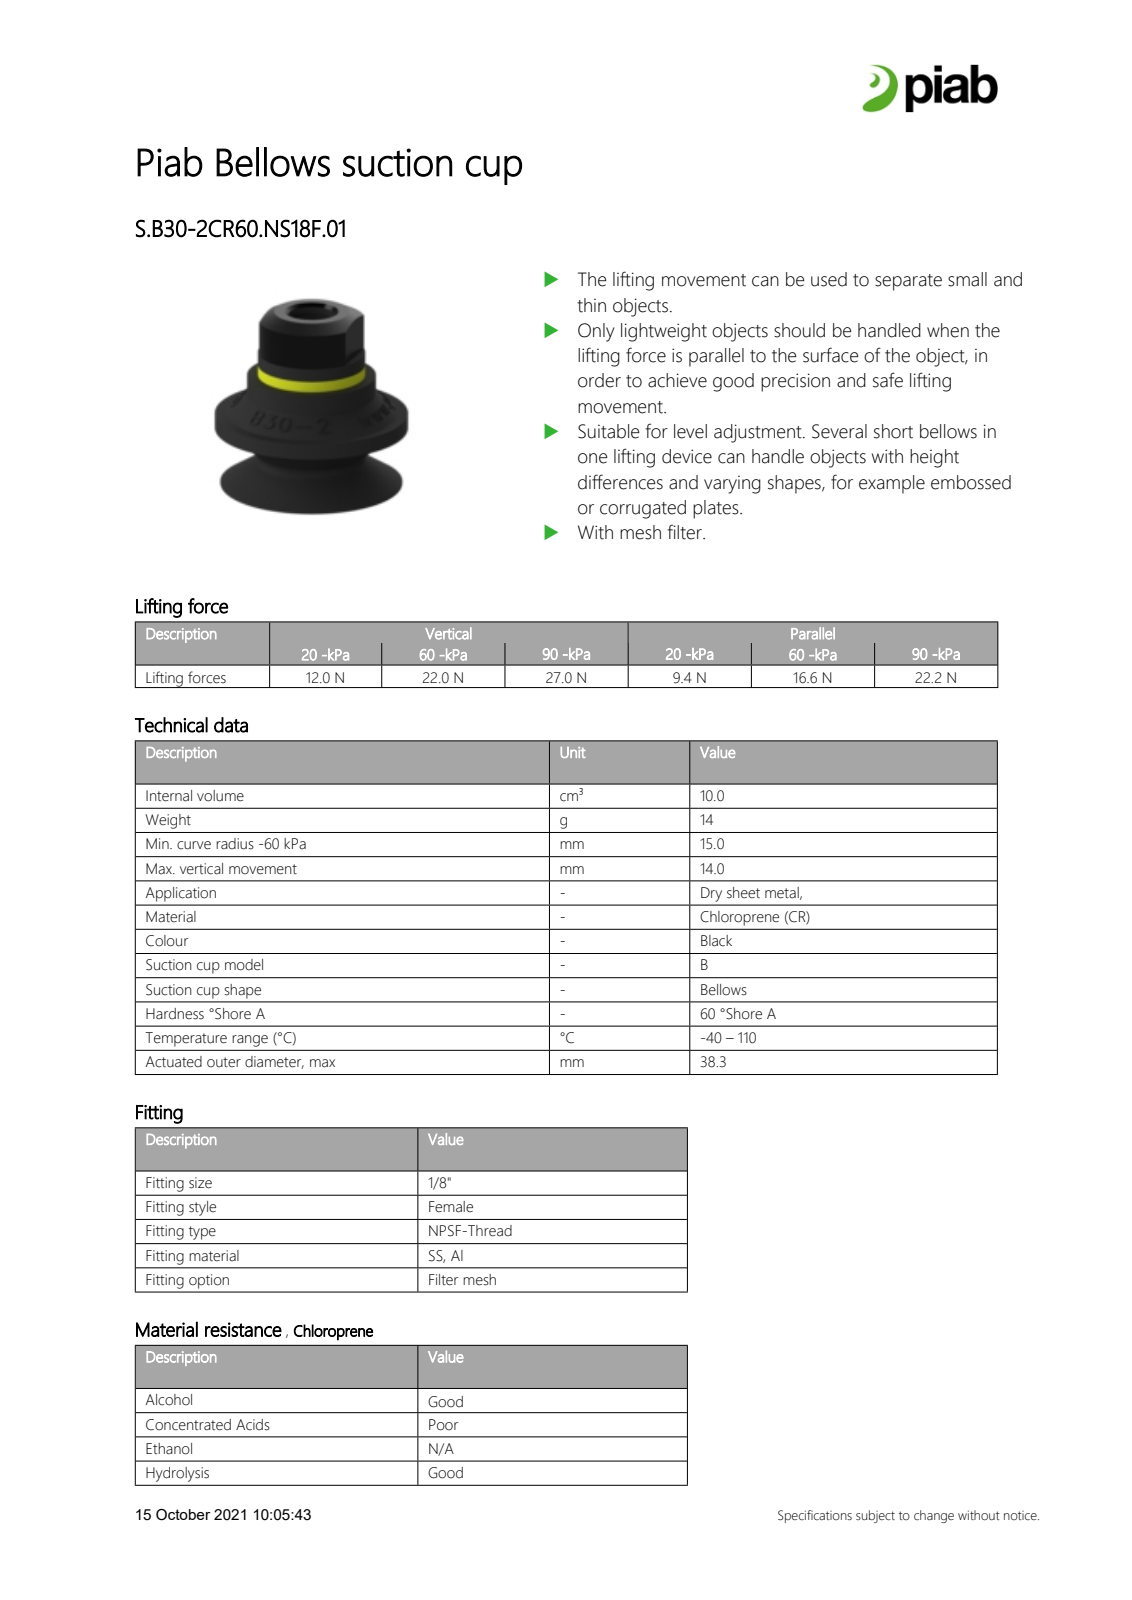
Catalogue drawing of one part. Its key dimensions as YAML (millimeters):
part_name: "S_A006_B012; A006_B30-2; B012_Fitting 40 04AA"
step_written_by: "ST-DEVELOPER v16.7 (AUTOMOTIVE_DESIGN)"
units: millimeters
bodies: {solids: 2, faces: 697, planar: 423, cylindrical: 59, other: 215}
overall_size: [36, 36, 34.2]
volume: 14145
surface_area: 7354
round_holes:
  - {diameter: 6.35, count: 1}
  - {diameter: 8.7, count: 1}
  - {diameter: 10, count: 1}
round_bosses_or_shafts:
  - {diameter: 36, count: 1}
  - {diameter: 34, count: 1}
  - {diameter: 24, count: 1}
  - {diameter: 20, count: 1}
partial_cylinders:
  - {radius: 0.5, count: 49}
face_to_face_distances: [14.2, 26.2, 12, 15, 8, 3, 11.2, 19.2, 5, 7]
